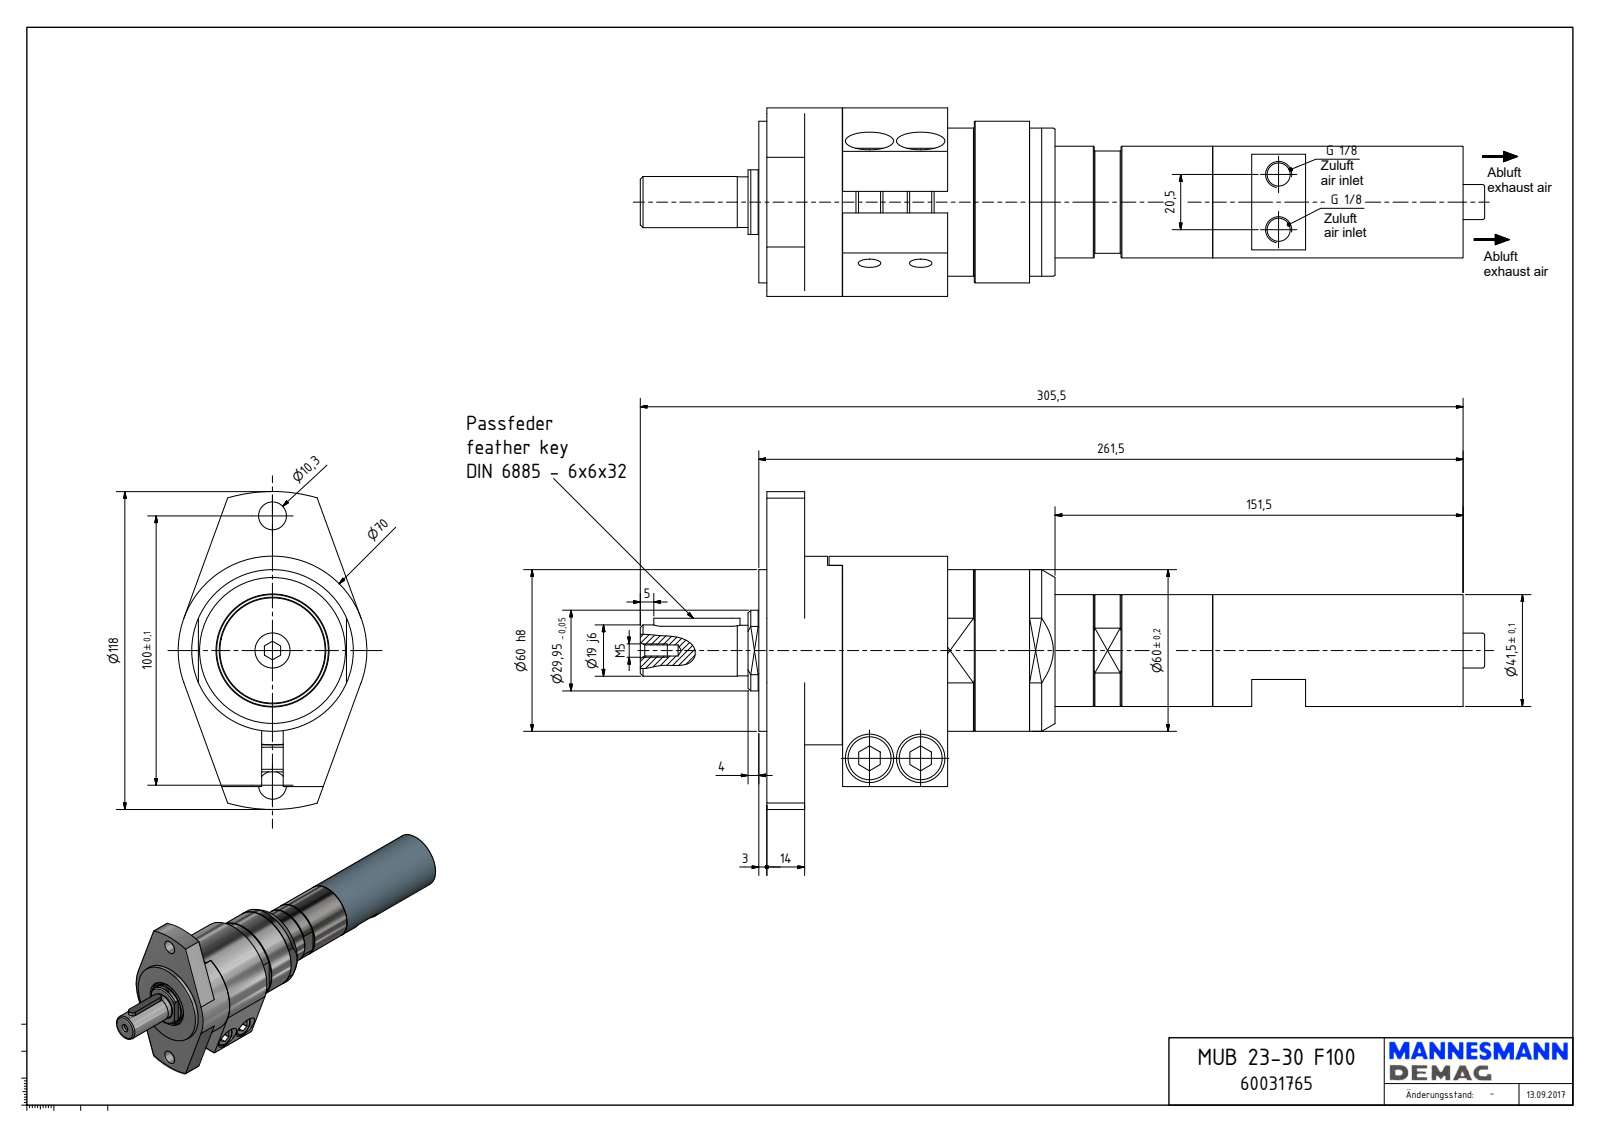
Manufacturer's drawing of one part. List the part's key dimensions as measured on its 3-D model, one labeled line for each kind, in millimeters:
Part name (STEP PRODUCT): MUB 23-30 F100_60031765
STEP written by: Autodesk Inventor 2018 (AUTOMOTIVE_DESIGN)
Units: millimetres
Bodies: 1 solid, 214 faces (109 planar, 68 cylindrical, 37 other)
Overall size (bounding box): 313.5 × 118 × 70
Volume: 642 899 mm³ · Surface area: 75 422 mm²
Round holes (diameter × count): ⌀4 ×3, ⌀2 ×2, ⌀3.2 ×2, ⌀3.5 ×2, ⌀5 ×2, ⌀8.38 ×2, ⌀8.57 ×2, ⌀10.3 ×2, ⌀10.5 ×2, ⌀18 ×2, ⌀1.55 ×1, ⌀4.13 ×1
Round bosses / shafts (diameter × count): ⌀16 ×2, ⌀10 ×2, ⌀70 ×1, ⌀60 ×1, ⌀41.5 ×1, ⌀39 ×1, ⌀29.95 ×1, ⌀19 ×1
Partial cylindrical surfaces — rounded edges, fillets, slot ends (radius × count): R1.6 ×2, R3 ×2, R6.84 ×1, R27.42 ×1, R29.17 ×1, R34.04 ×1, R59 ×1
Main face-to-face distances: 14, 17, 3, 39, 70.1, 67.1, 53.1, 31.1, 28.1, 14.1
Hole centre spacings: 16.76, 4.94, 7.67, 11.9, 12.5, 12.94, 17.13, 21.45
